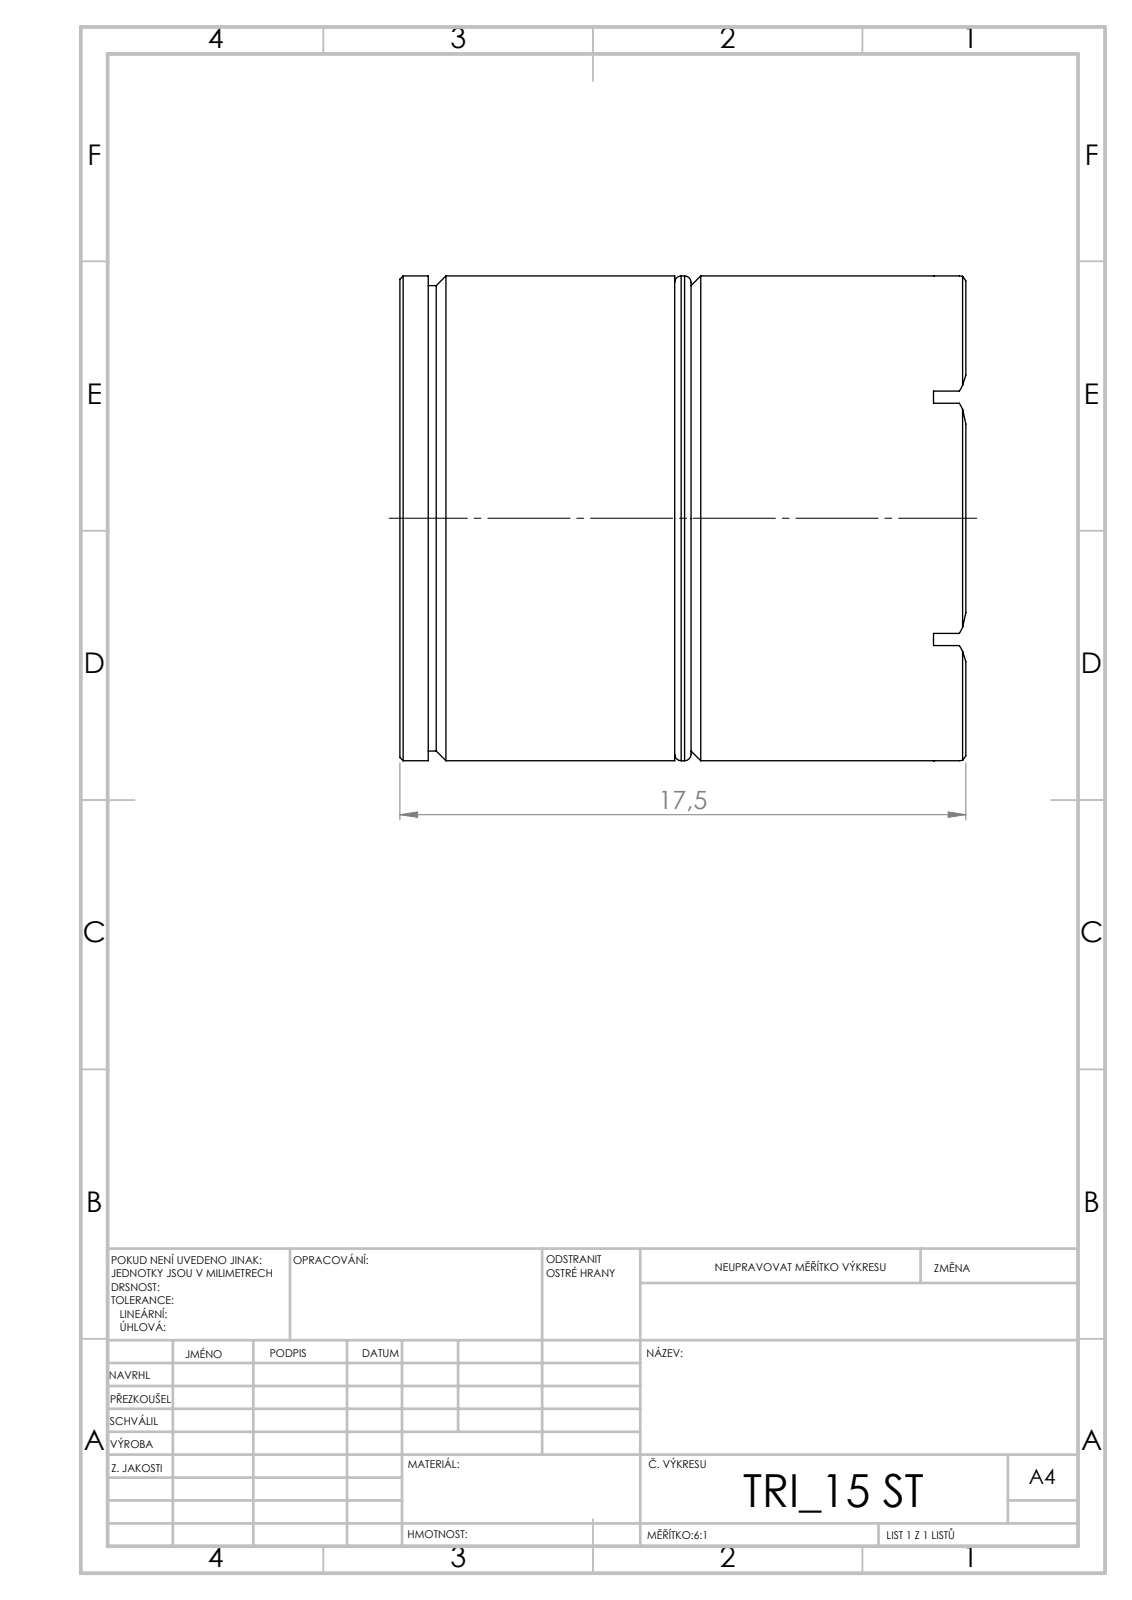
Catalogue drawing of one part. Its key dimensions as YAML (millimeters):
step_written_by: "SolidWorks 2019 (CONFIG_CONTROL_DESIGN)"
units: millimeters
bodies: {solids: 2, faces: 53, planar: 24, cylindrical: 12, other: 17}
overall_size: [17.5, 15, 15]
volume: 3013
surface_area: 1613
round_bosses_or_shafts:
  - {diameter: 15, count: 1}
  - {diameter: 14.4, count: 1}
face_to_face_distances: [8.5, 9, 0.5, 7.5, 8, 16.5, 13.2, 1, 17.5, 16.63]
